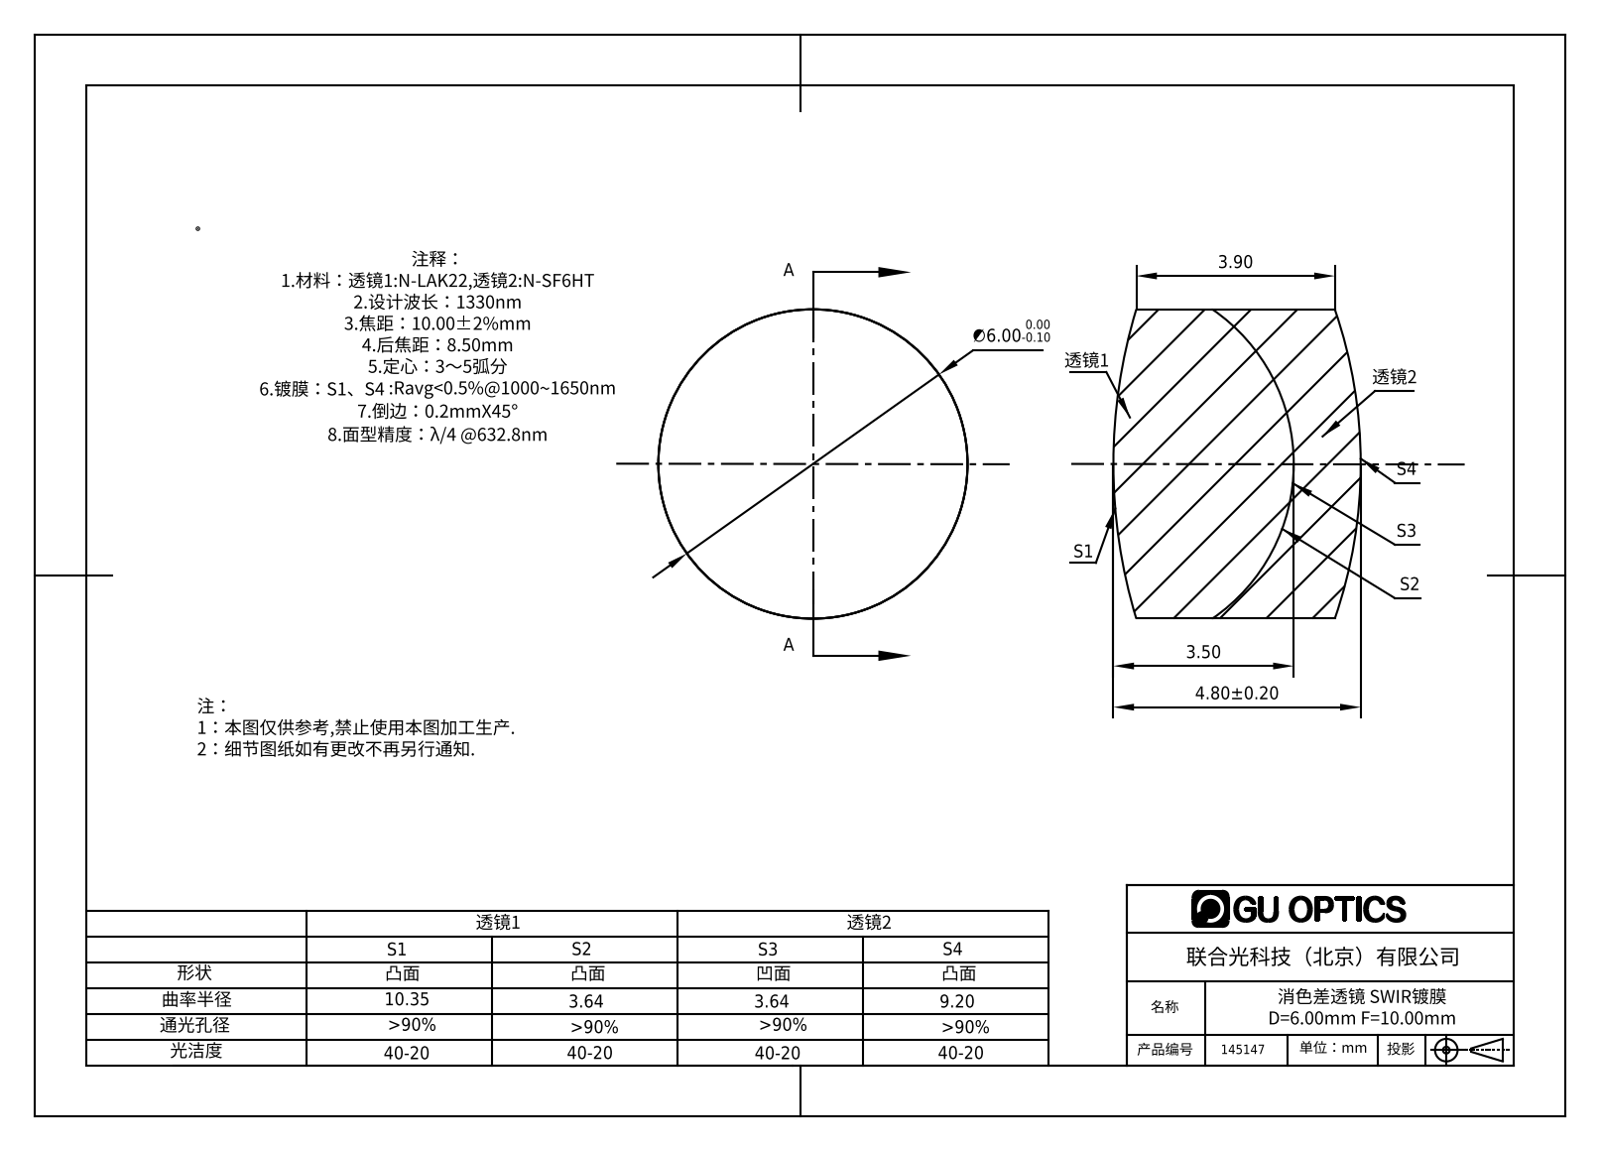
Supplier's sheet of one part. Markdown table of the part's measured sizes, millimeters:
| quantity | value |
| --- | --- |
| part name | 145147 |
| STEP written by | SolidWorks 2016 (AUTOMOTIVE_DESIGN) |
| units | millimeters |
| bodies | 2 solids, 12 faces (0 planar, 4 cylindrical, 8 other) |
| overall size | 6 × 6 × 4.8 |
| volume | 122 mm³ |
| surface area | 203 mm² |
| round bosses / shafts (diameter × count) | 6 × 1 |
